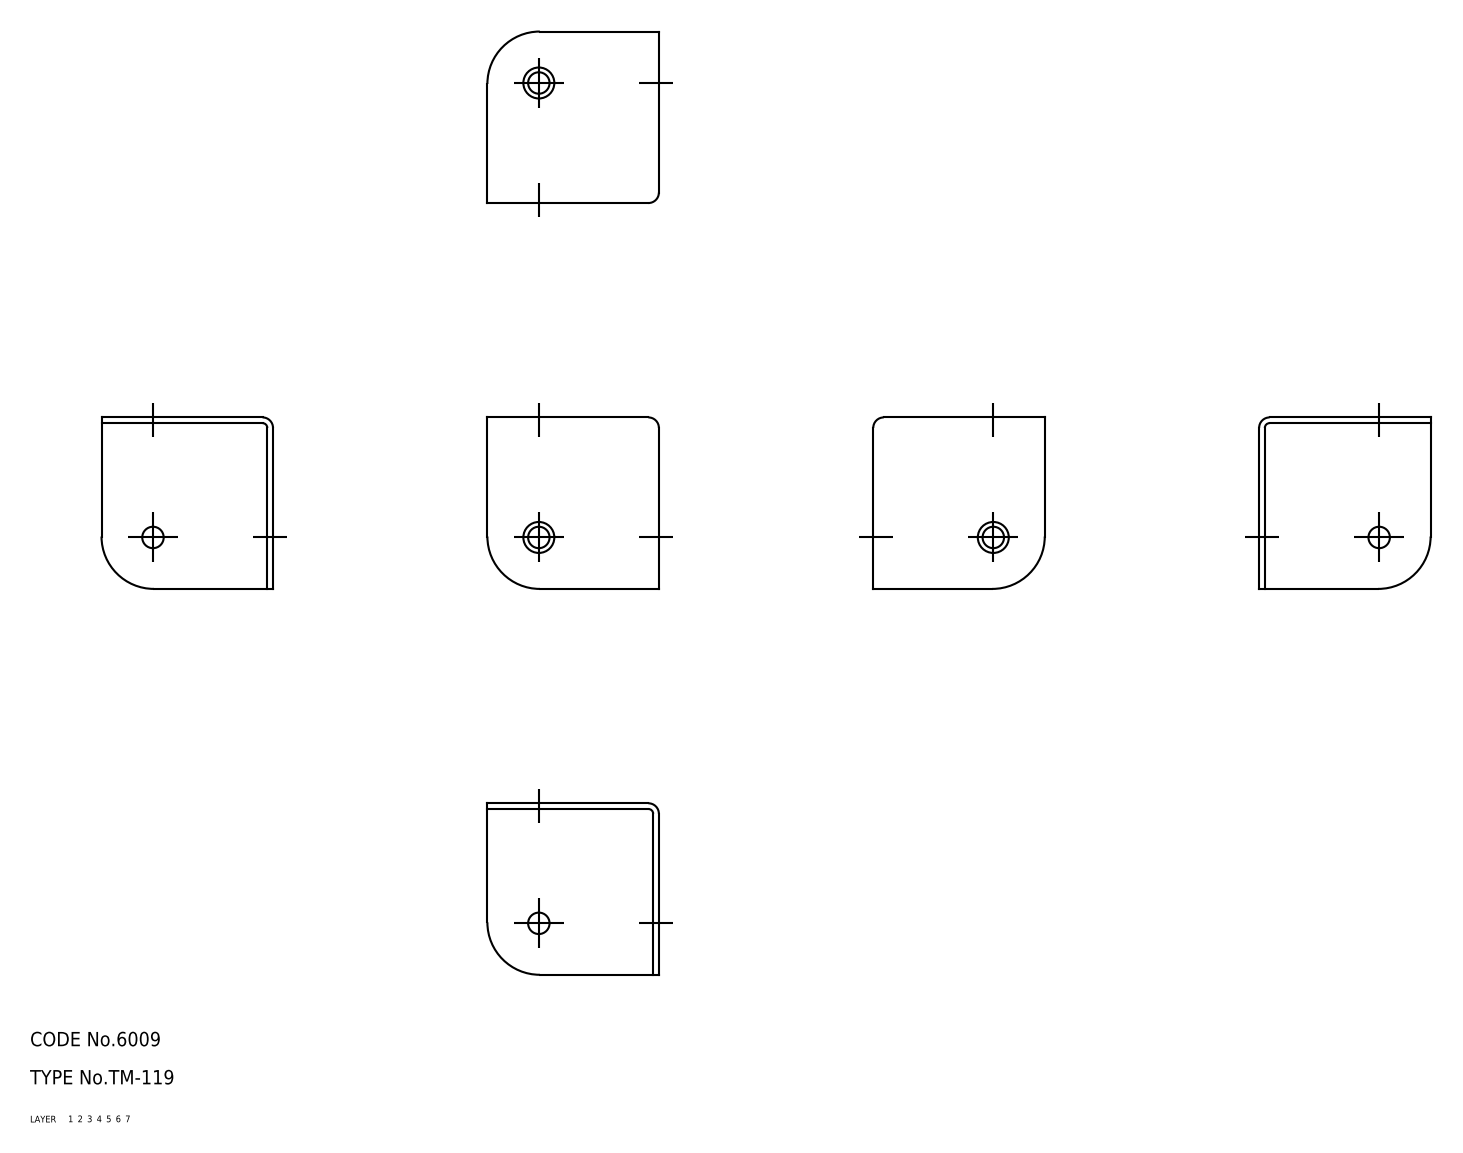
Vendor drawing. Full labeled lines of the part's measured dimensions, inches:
Part name (STEP PRODUCT): angle
STEP written by: CADfix (AUTOMOTIVE_DESIGN)
Units: inches
Bodies: 1 solid, 32 faces (0 planar, 0 cylindrical, 32 other)
Overall size (bounding box): 1.417 × 1.417 × 1.417
Volume: 0.259 in³ · Surface area: 11.45 in²
